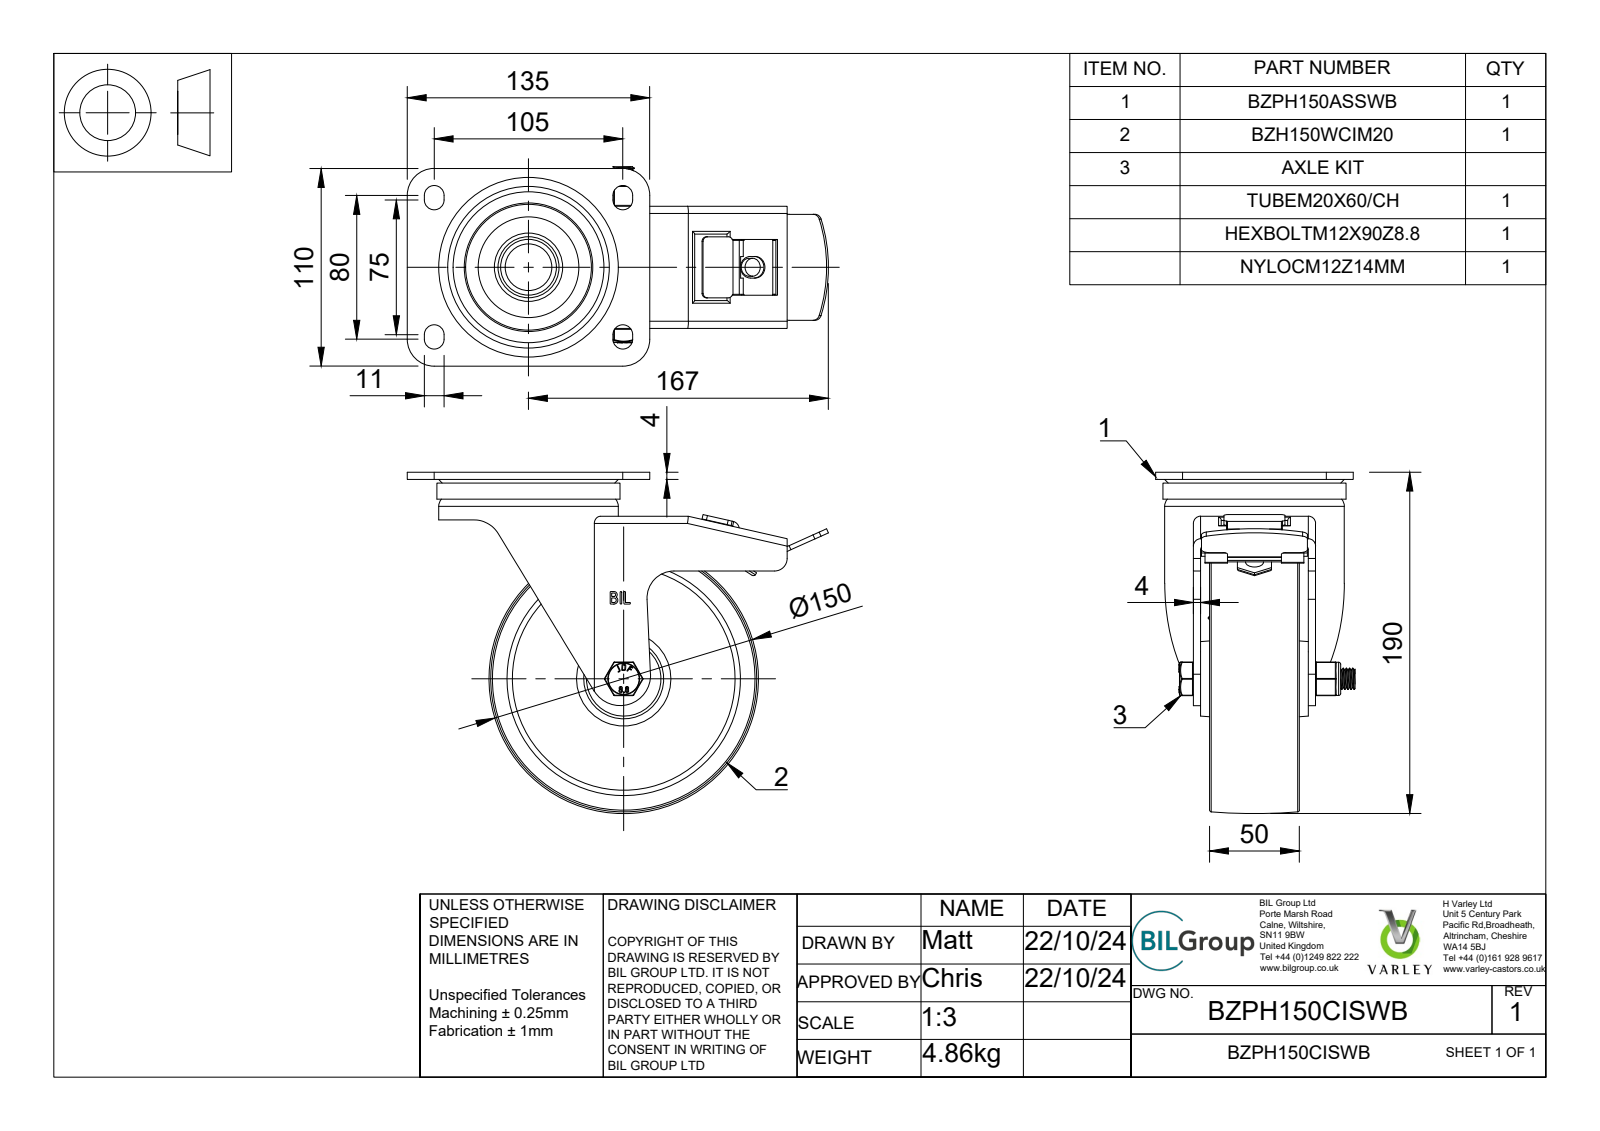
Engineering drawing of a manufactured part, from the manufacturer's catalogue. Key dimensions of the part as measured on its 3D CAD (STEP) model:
Part name (STEP PRODUCT): BZPH150CISWB v3; BZPH150ASSWB v1; ZINC PLATED, PRESSED STEEL TOP PLATE; ZINC PLATED, PRESSED STEEL FORKS (+8 more)
STEP written by: Autodesk Translation Framework v13.20.0.188 (AUTOMOTIVE_DESIGN)
Units: millimetres
Bodies: 13 solids, 580 faces (265 planar, 191 cylindrical, 124 other)
Overall size (bounding box): 234.5 × 190 × 111
Volume: 672 077 mm³ · Surface area: 233 756 mm²
Round holes (diameter × count): ⌀5 ×1, ⌀10 ×1, ⌀12 ×1, ⌀12.1 ×1, ⌀12.5 ×1, ⌀14 ×1, ⌀20.2 ×1, ⌀26 ×1, ⌀42.2 ×1, ⌀52 ×1, ⌀62 ×1, ⌀92 ×1
Round bosses / shafts (diameter × count): ⌀101.95 ×1, ⌀100 ×1, ⌀73 ×1, ⌀50 ×1, ⌀19.9 ×1, ⌀18.5 ×1, ⌀17.75 ×1, ⌀11.83 ×1
Partial cylindrical surfaces — rounded edges, fillets, slot ends (radius × count): R0.5 ×22, R1.5 ×13, R4 ×9, R5.5 ×8, R1.25 ×6, R2 ×6, R2.5 ×6, R1 ×5
Main face-to-face distances: 4, 9, 25, 35, 10, 29, 39, 64, 1, 30
